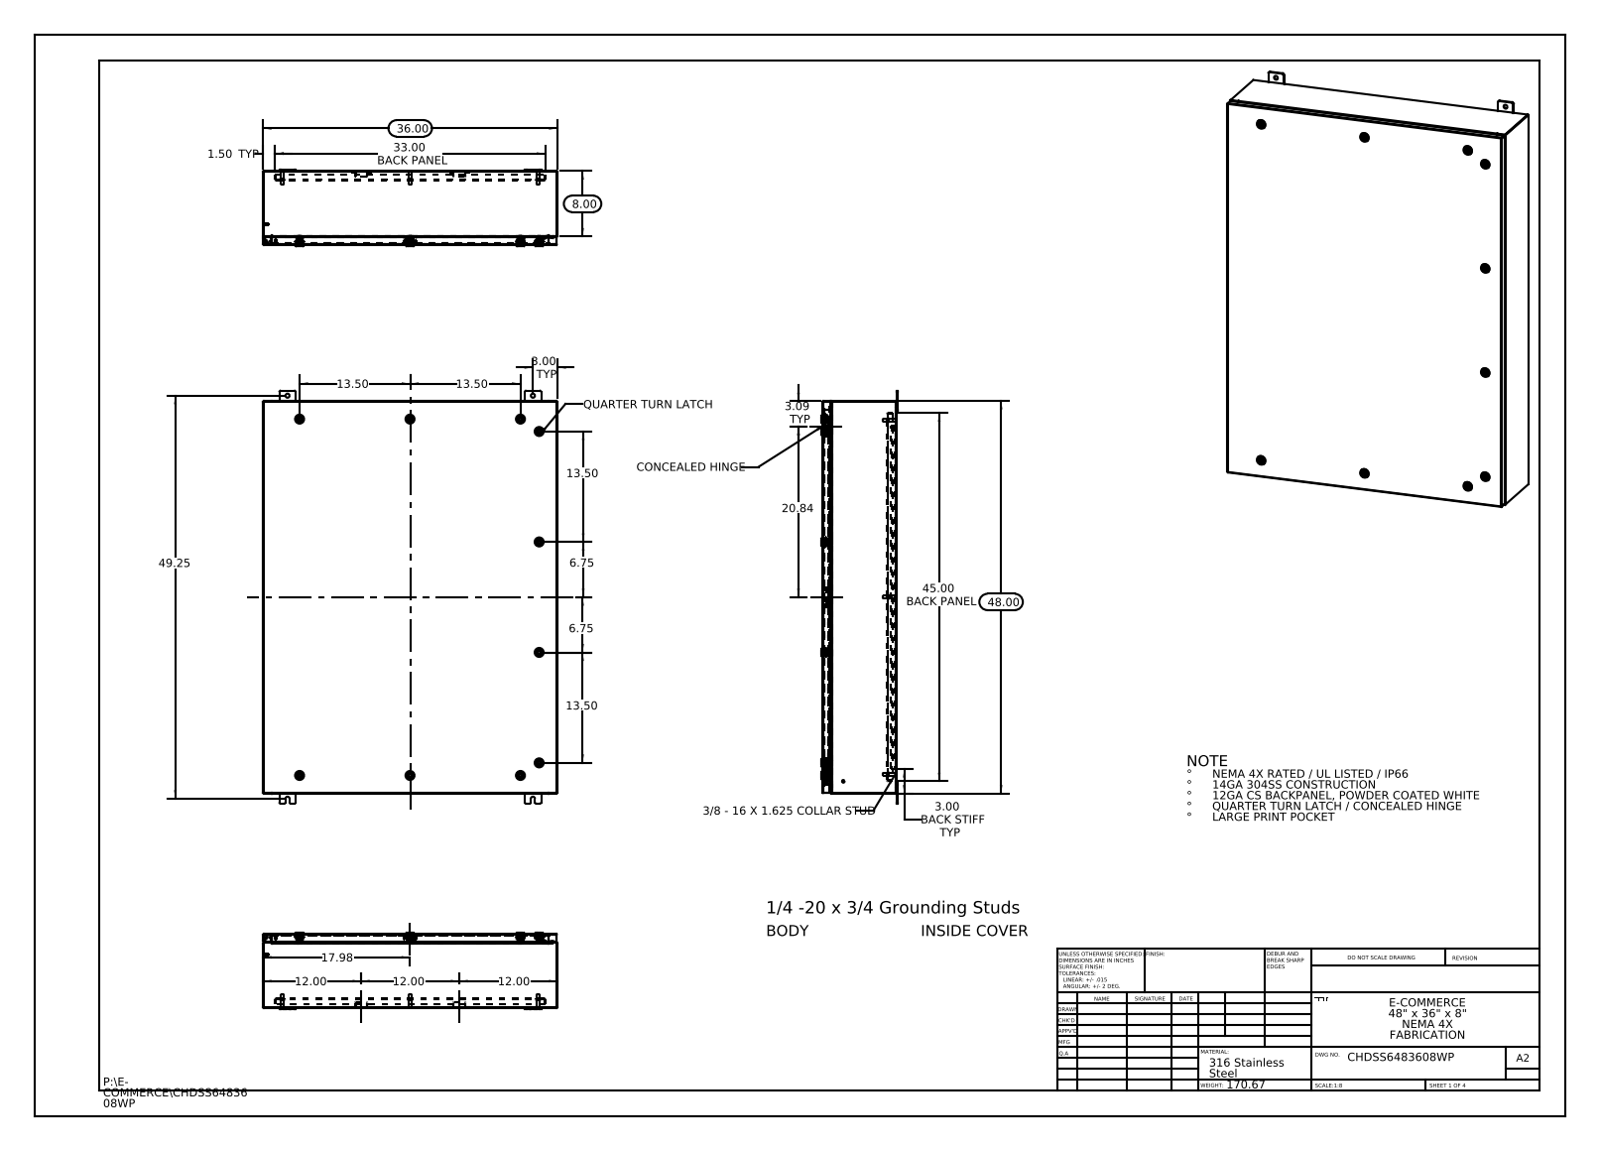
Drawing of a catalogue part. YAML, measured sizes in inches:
part_name: "HW-CLH-R001-0500_2412-026240-2445-Industrilas; CHDSS6483608WP Top; Washer-221320-IB-Industrilas_Washer-221320-IB-Industrilas; HW-CLH-E5-8004_Cam-232112-U-Industrilas (+8 more)"
step_written_by: "SolidWorks 2013 (CONFIG_CONTROL_DESIGN)"
units: inches
bodies: {solids: 94, faces: 9060, planar: 2626, cylindrical: 2826, other: 3608}
overall_size: [50.5, 36, 9.356]
volume: 603.3
surface_area: 14901
round_holes:
  - {diameter: 0.5, count: 12}
  - {diameter: 0.197, count: 10}
  - {diameter: 0.394, count: 10}
  - {diameter: 0.4, count: 10}
  - {diameter: 0.63, count: 10}
  - {diameter: 0.787, count: 10}
  - {diameter: 0.136, count: 6}
  - {diameter: 0.25, count: 6}
  - {diameter: 0.211, count: 1}
round_bosses_or_shafts:
  - {diameter: 0.236, count: 12}
  - {diameter: 1.102, count: 10}
  - {diameter: 0.78, count: 10}
  - {diameter: 0.626, count: 10}
  - {diameter: 0.61, count: 10}
  - {diameter: 0.531, count: 10}
  - {diameter: 0.392, count: 10}
  - {diameter: 0.114, count: 10}
partial_cylinders:
  - {radius: 0.006, count: 330}
  - {radius: 0.118, count: 330}
  - {radius: 0.028, count: 120}
  - {radius: 0.02, count: 40}
  - {radius: 0.197, count: 40}
  - {radius: 0.013, count: 34}
  - {radius: 0.088, count: 30}
  - {radius: 0.19, count: 24}
face_to_face_distances: [0.075, 0.074, 8.861, 8.936, 9.01, 8.935, 0.104, 1, 1.075, 7.861]
hole_center_spacings: [13.5, 20, 20.123, 21.625, 27, 38.003, 45.594, 45.986]
